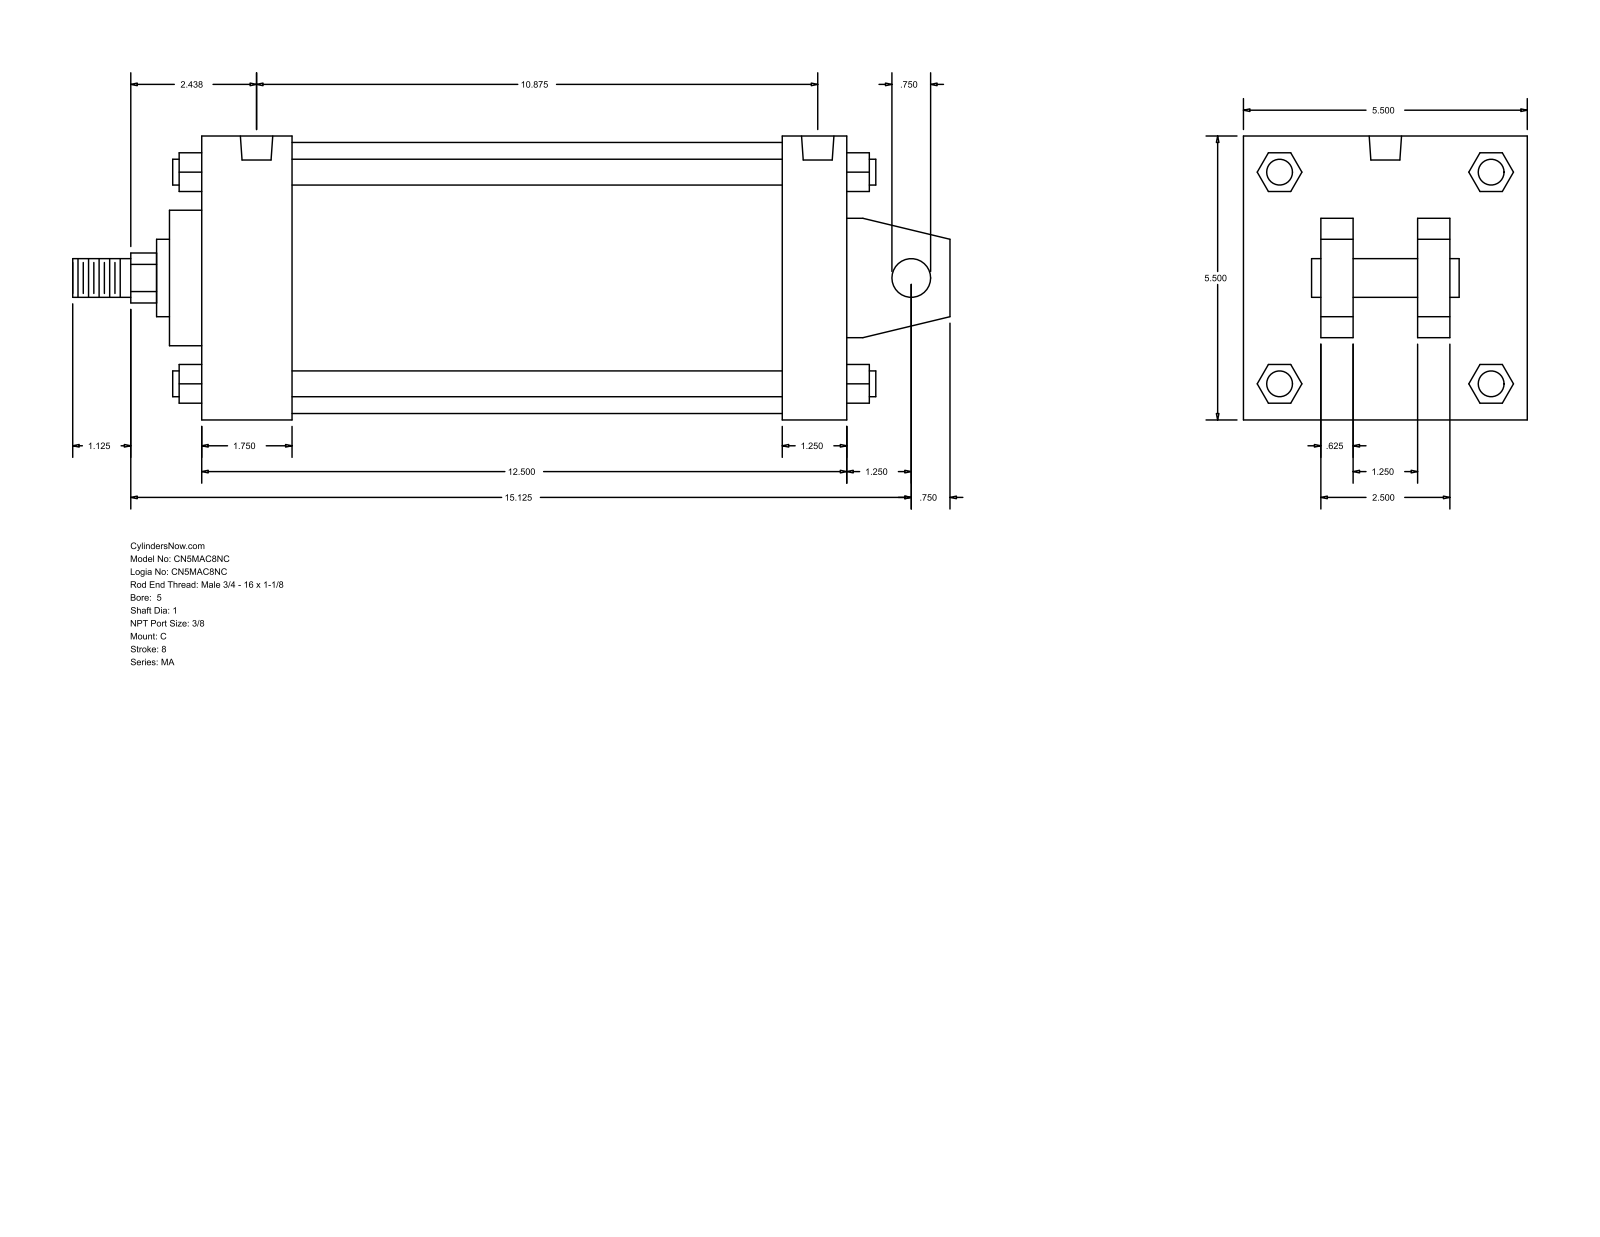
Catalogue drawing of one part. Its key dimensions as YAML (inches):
part_name: "MA_C__0500_1"
step_written_by: "GSSL Pune (CONFIG_CONTROL_DESIGN)"
units: inches
bodies: {solids: 0, faces: 141, planar: 109, cylindrical: 32, other: 0}
overall_size: [17, 5.5, 5.5]
round_holes:
  - {diameter: 0.437, count: 4}
  - {diameter: 0.627, count: 2}
round_bosses_or_shafts:
  - {diameter: 0.5, count: 4}
  - {diameter: 0.75, count: 2}
  - {diameter: 5.25, count: 1}
  - {diameter: 2.625, count: 1}
  - {diameter: 1.5, count: 1}
  - {diameter: 1, count: 1}
partial_cylinders:
  - {radius: 0.484, count: 1}
face_to_face_distances: [5.5, 12.5, 0.625, 11.25, 1.25, 1.75, 9.5, 10.75, 1.5, 4]
hole_center_spacings: [0.187, 10.5, 10.688, 10.875]
